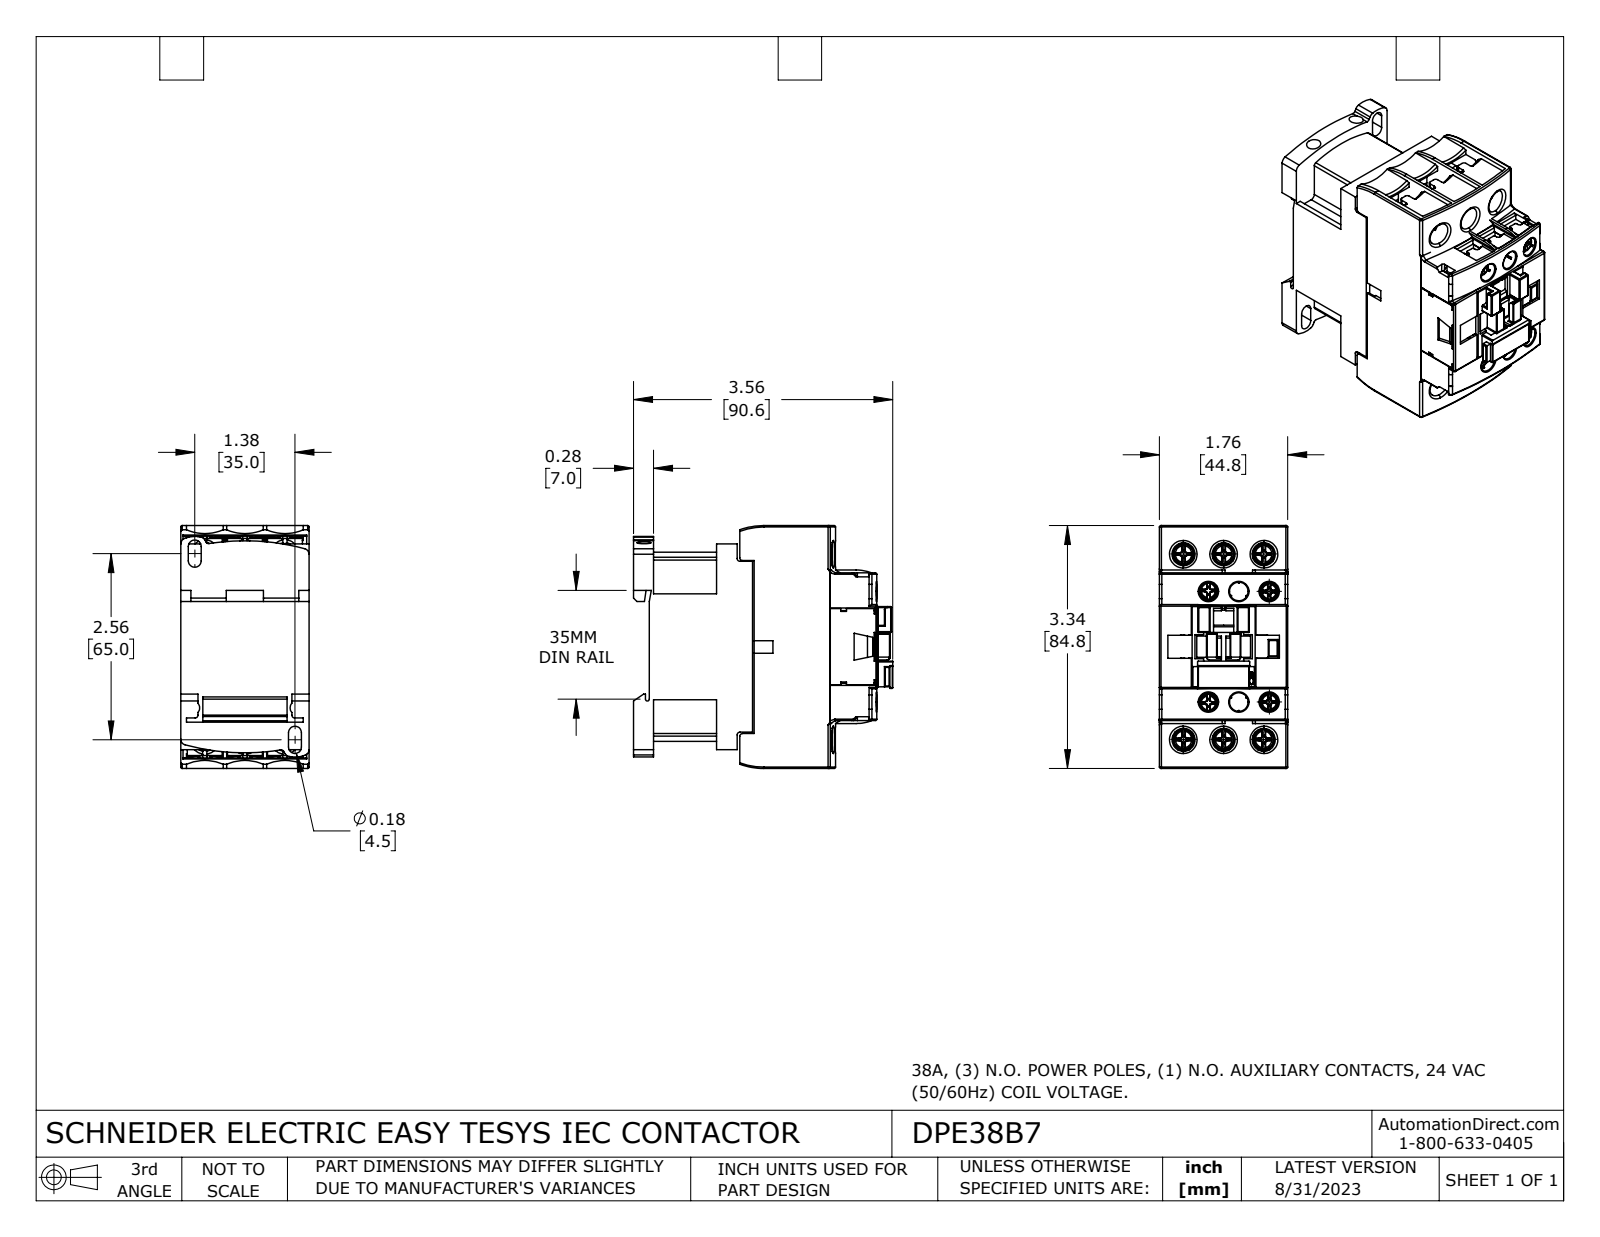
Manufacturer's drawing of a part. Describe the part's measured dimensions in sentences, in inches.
The part is named "DPE38B7". Its 3-D file was written by "SolidWorks 2021 (CONFIG_CONTROL_DESIGN)". It is 16 solids with 2674 faces: 1724 planar, 584 cylindrical and 366 other. Overall it measures 3.565 by 3.339 by 1.764 inches. Its volume is 12.56 cubic inches and its surface area 100.4 square inches. Round holes: 6 of diameter 0.256, 6 of diameter 0.315, 2 of diameter 0.197. Round bosses or shafts: 8 of diameter 0.157, 6 of diameter 0.126, 4 of diameter 0.138, 4 of diameter 0.134, 4 of diameter 0.108, 3 of diameter 0.394. Partial cylindrical surfaces (rounded edges, fillets, slot ends): 58 of radius 0.012, 36 of radius 0.006, 36 of radius 0.039, 34 of radius 0.02, 18 of radius 0.63, 17 of radius 0.008, 9 of radius 0.079, 8 of radius 0.031. The main face-to-face distances are 1.764, 0.551, 0.022, 0.059, 1.089, 1.067, 0.047, 0.031, 1.382, 1.419. The hole center spacings are 0.417, 0.551, 1.576, 2.61, 1.52, 2.551, 0.553, 0.56.
